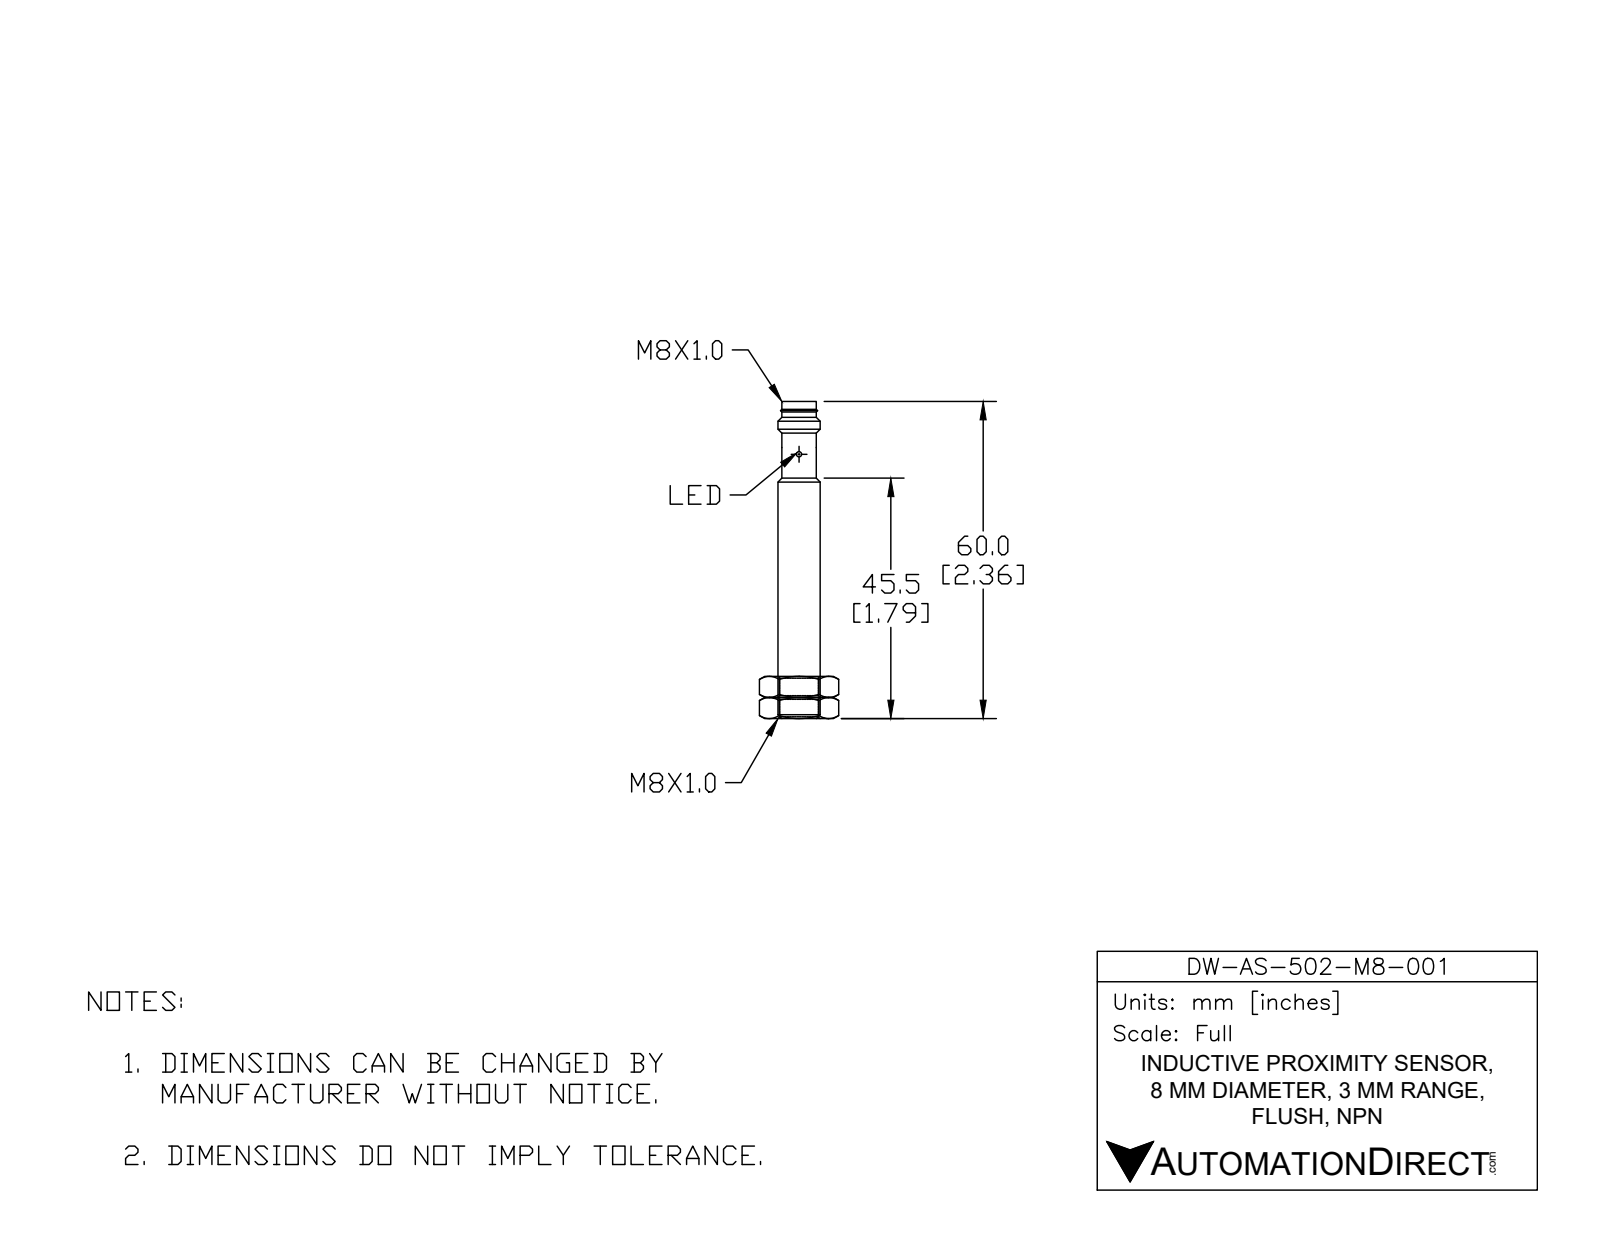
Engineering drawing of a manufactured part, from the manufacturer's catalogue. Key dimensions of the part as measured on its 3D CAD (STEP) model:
Part name (STEP PRODUCT): DW-AS-502-M8-001
STEP written by: SolidWorks 2017 (AUTOMOTIVE_DESIGN)
Units: inches
Bodies: 1 solid, 36 faces (7 planar, 17 cylindrical, 12 other)
Overall size (bounding box): 2.362 × 0.315 × 0.315
Volume: 0.163 in³ · Surface area: 2.629 in²
Round holes (diameter × count): ⌀0.071 ×2
Round bosses / shafts (diameter × count): ⌀0.039 ×3, ⌀0.315 ×1, ⌀0.272 ×1, ⌀0.256 ×1, ⌀0.236 ×1
Main face-to-face distances: 2.161, 2.165, 2.362, 2.358, 0.197, 2.323, 2.319, 0.157, 0.039
